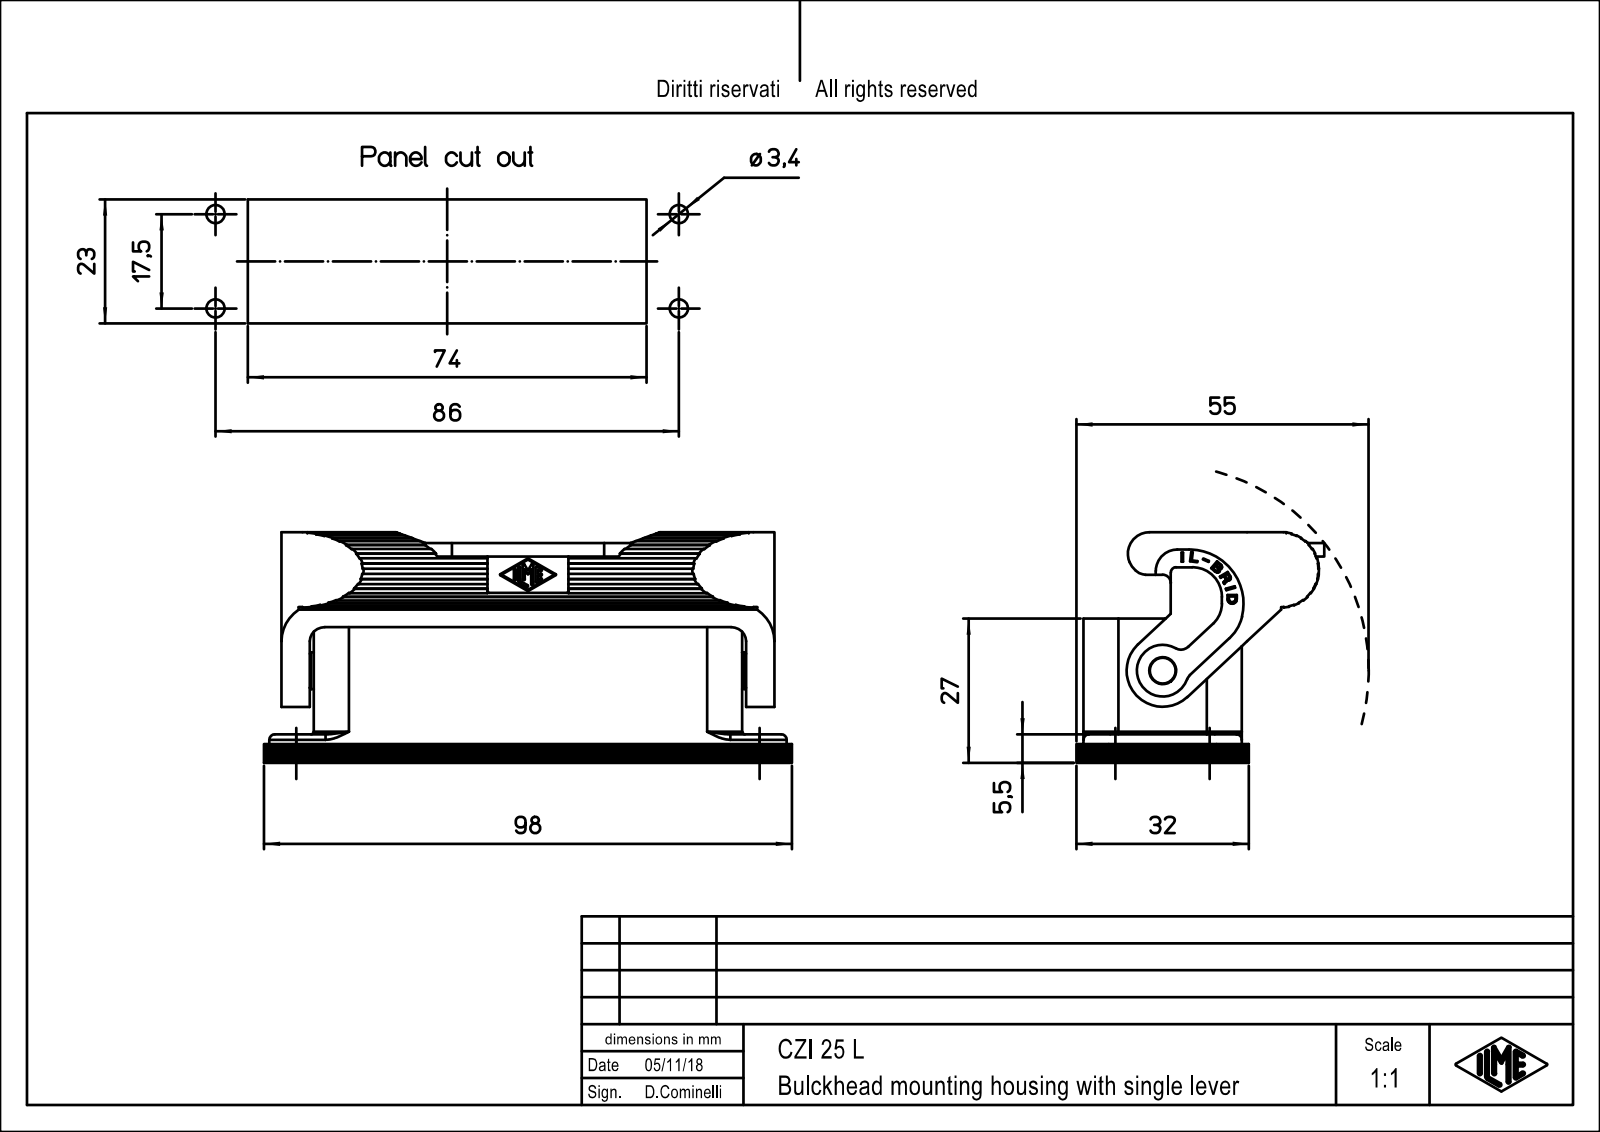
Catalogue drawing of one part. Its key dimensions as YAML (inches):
part_name: "CZI_25_L"
step_written_by: "PTC Creo Elements/Direct Modeling 19.0E 27-Jun-2016 (C) Parametric Technology GmbH (AUTOMOTIVE_DESIGN)"
units: inches
bodies: {solids: 1, faces: 373, planar: 182, cylindrical: 171, other: 20}
overall_size: [3.858, 1.811, 1.685]
volume: 2.137
surface_area: 35.47
round_holes:
  - {diameter: 0.118, count: 4}
  - {diameter: 0.126, count: 4}
  - {diameter: 0.134, count: 4}
  - {diameter: 0.197, count: 1}
round_bosses_or_shafts:
  - {diameter: 0.268, count: 1}
  - {diameter: 0.189, count: 1}
partial_cylinders:
  - {radius: 0.008, count: 15}
  - {radius: 0.039, count: 5}
  - {radius: 0.118, count: 5}
  - {radius: 0.197, count: 5}
  - {radius: 0.098, count: 4}
  - {radius: 0.138, count: 4}
  - {radius: 0.236, count: 4}
  - {radius: 0.256, count: 4}
face_to_face_distances: [0.102, 1.055, 1.157, 0.953, 1.307, 1.205, 0.252, 0.15, 0.138, 0.207]
hole_center_spacings: [0.395, 0.768, 2.992, 3.064, 0.63, 0.689, 2.598, 2.674]
